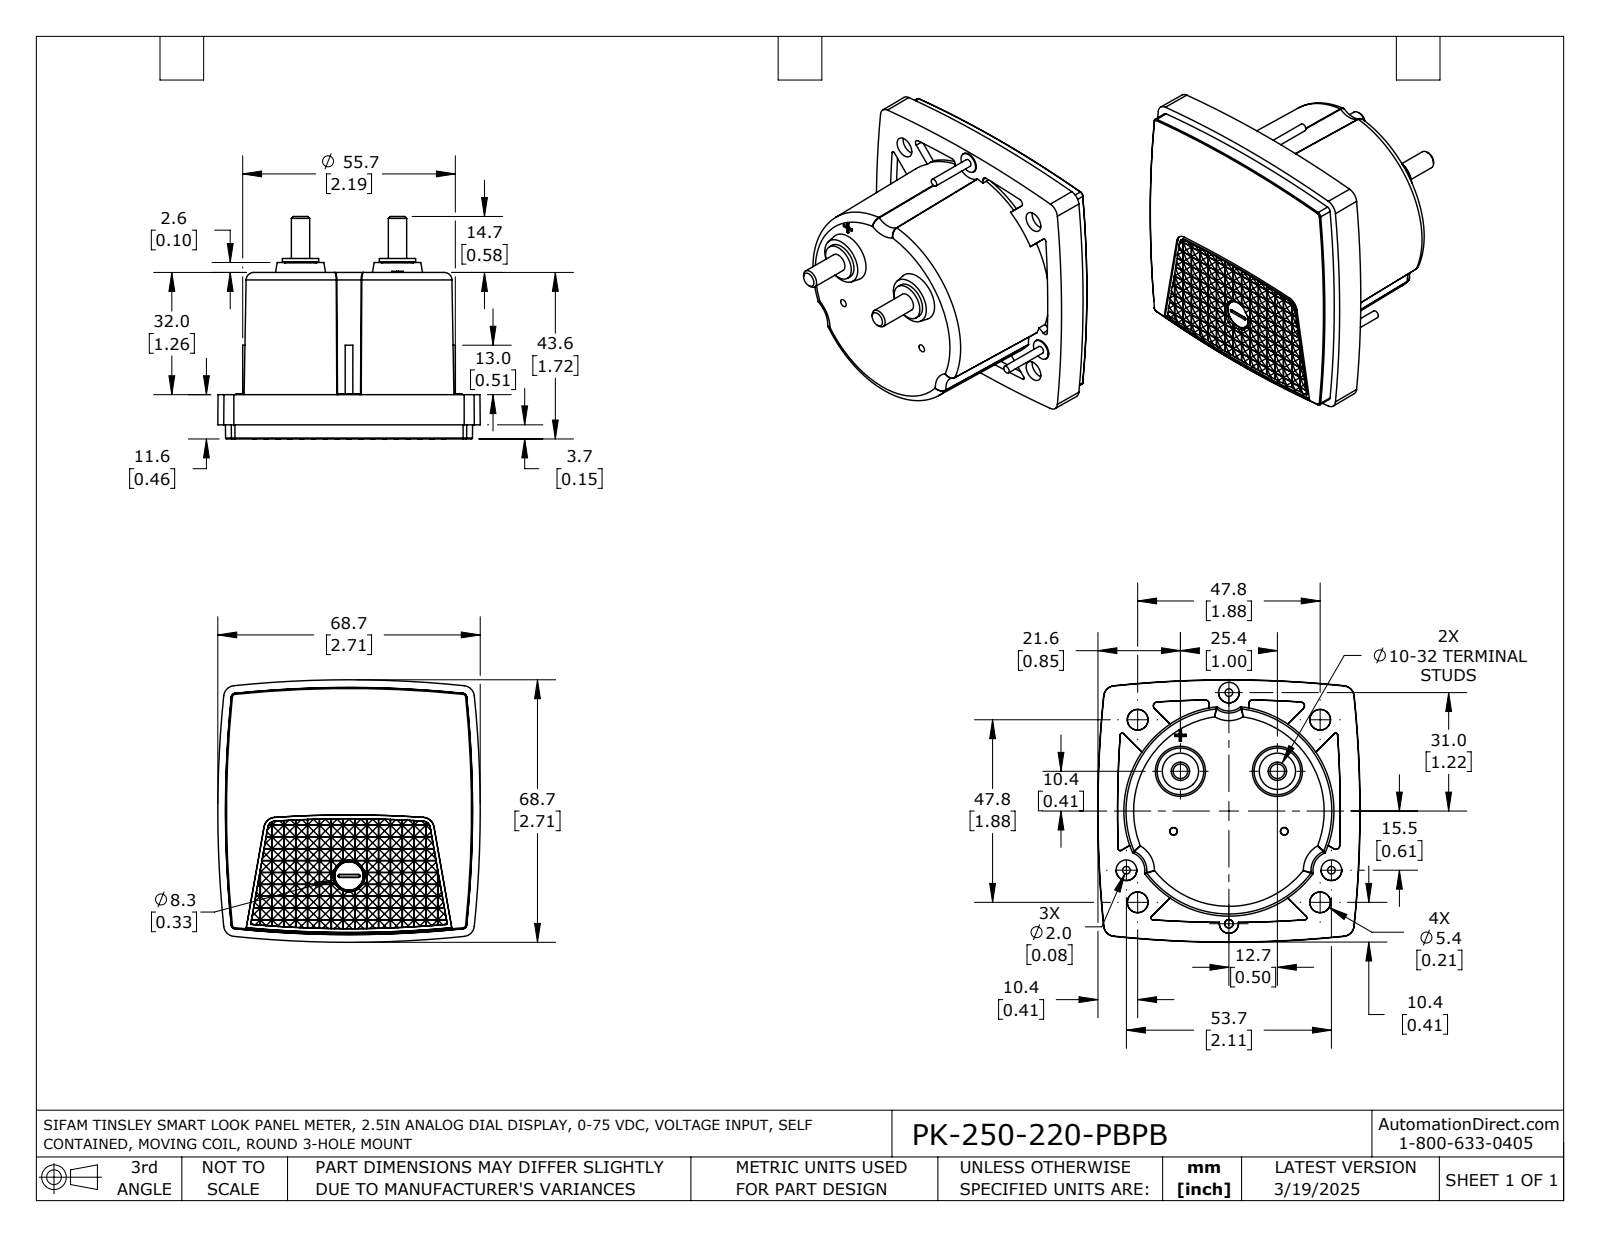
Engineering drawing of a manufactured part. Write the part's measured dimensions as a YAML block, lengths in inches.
part_name: "PK-250-220-PBPB"
step_written_by: "SolidWorks 2021 (AUTOMOTIVE_DESIGN)"
units: inches
bodies: {solids: 1, faces: 1550, planar: 1165, cylindrical: 265, other: 120}
overall_size: [2.706, 2.706, 2.297]
volume: 7.594
surface_area: 30.41
round_bosses_or_shafts:
  - {diameter: 0.213, count: 3}
  - {diameter: 0.079, count: 3}
  - {diameter: 0.374, count: 2}
  - {diameter: 0.189, count: 2}
  - {diameter: 0.215, count: 1}
partial_cylinders:
  - {radius: 0.167, count: 2}
  - {radius: 1.083, count: 1}
face_to_face_distances: [1.717, 1.26, 0.457, 0.024, 0.087, 0.096, 0.311, 0.12, 0.072, 1.346]
